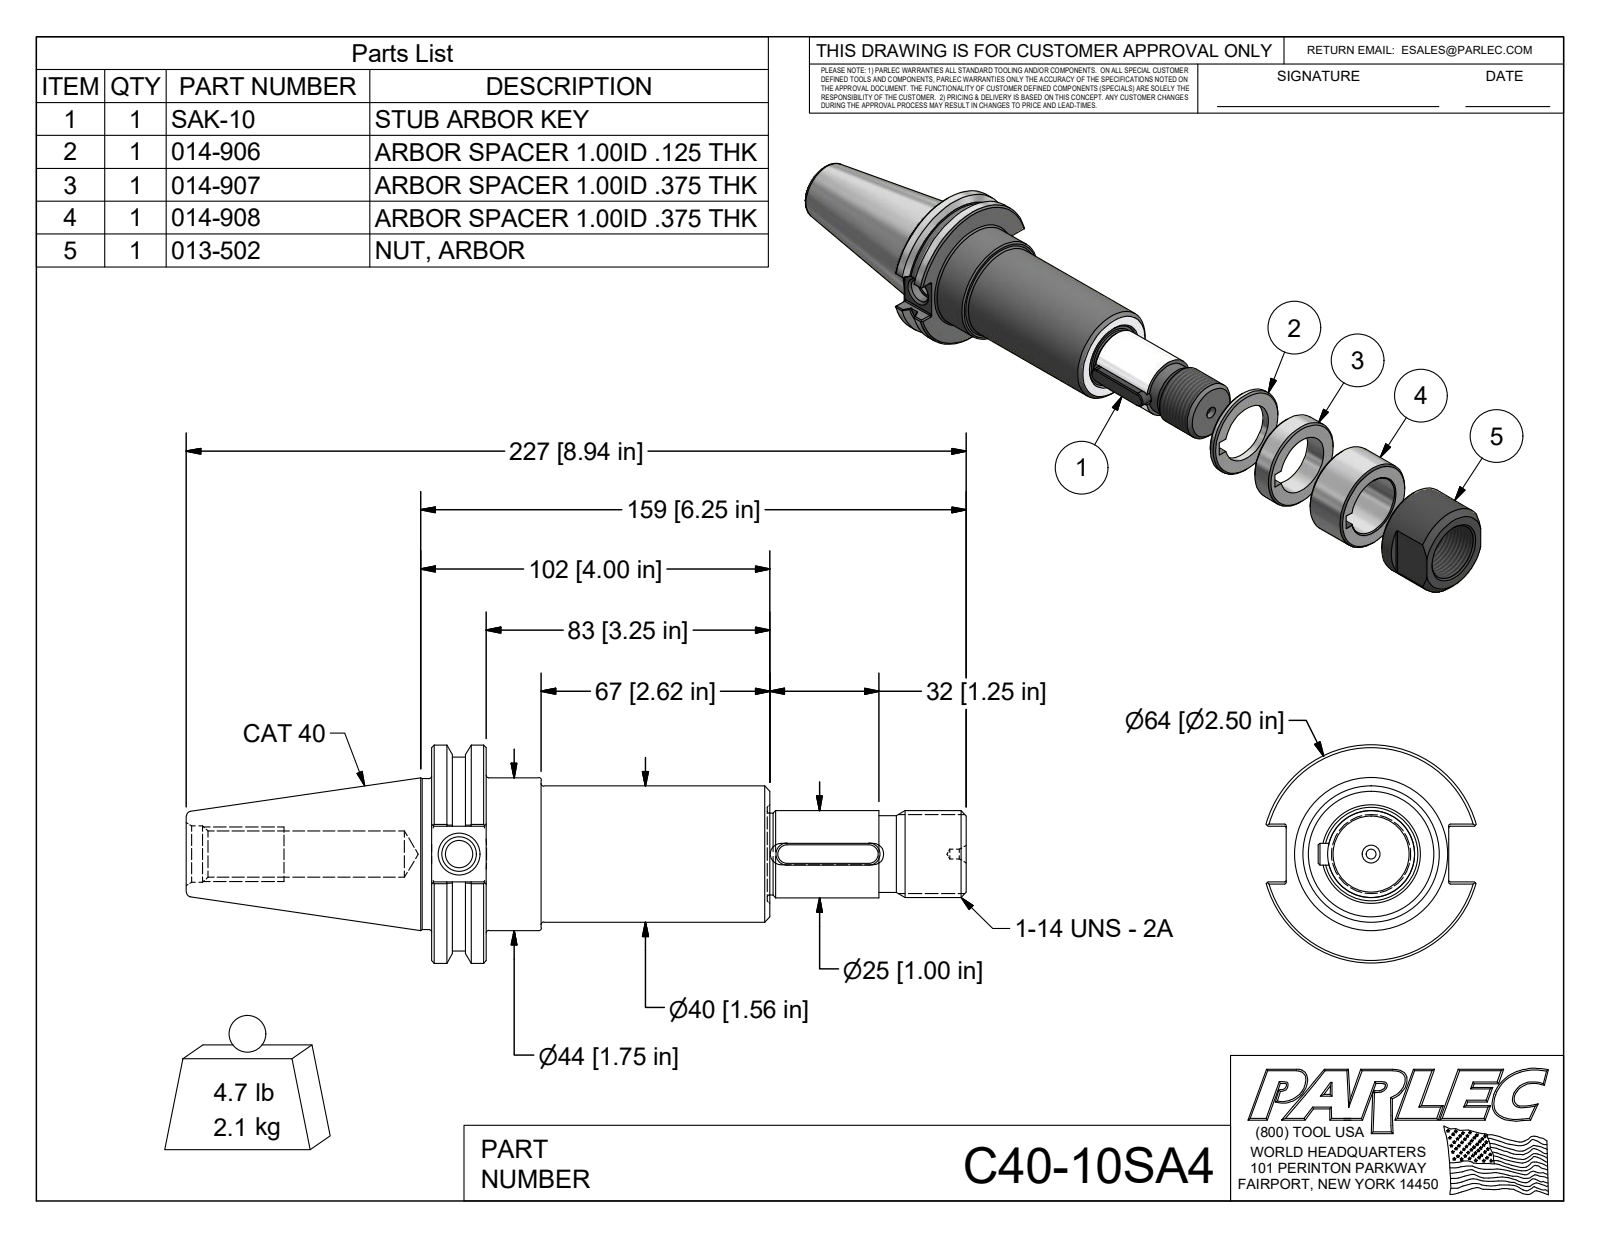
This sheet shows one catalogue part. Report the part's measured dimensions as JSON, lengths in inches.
{"part_name": "C40-10SA4; SAK-10", "step_written_by": "Autodesk Inventor 2018 (AUTOMOTIVE_DESIGN)", "units": "inches", "bodies": {"solids": 2, "faces": 120, "planar": 46, "cylindrical": 34, "other": 40}, "overall_size": [8.937, 2.5, 2.406], "volume_in3": 14.55, "surface_area_in2": 54.98, "round_holes": [[0.109, 1], [0.315, 1], [0.399, 1], [0.527, 1], [0.648, 1]], "round_bosses_or_shafts": [[2.5, 1], [2.219, 1], [1.75, 1], [1.73, 1], [1.56, 1], [1, 1], [0.993, 1], [0.94, 1]], "partial_cylinders_radius": [[0.02, 12], [0.124, 2], [0.125, 2]], "face_to_face_distances": [0.625, 3.875, 3.25, 6.125, 5.5, 2.25, 0.25, 1.243, 0.196, 0.444]}
